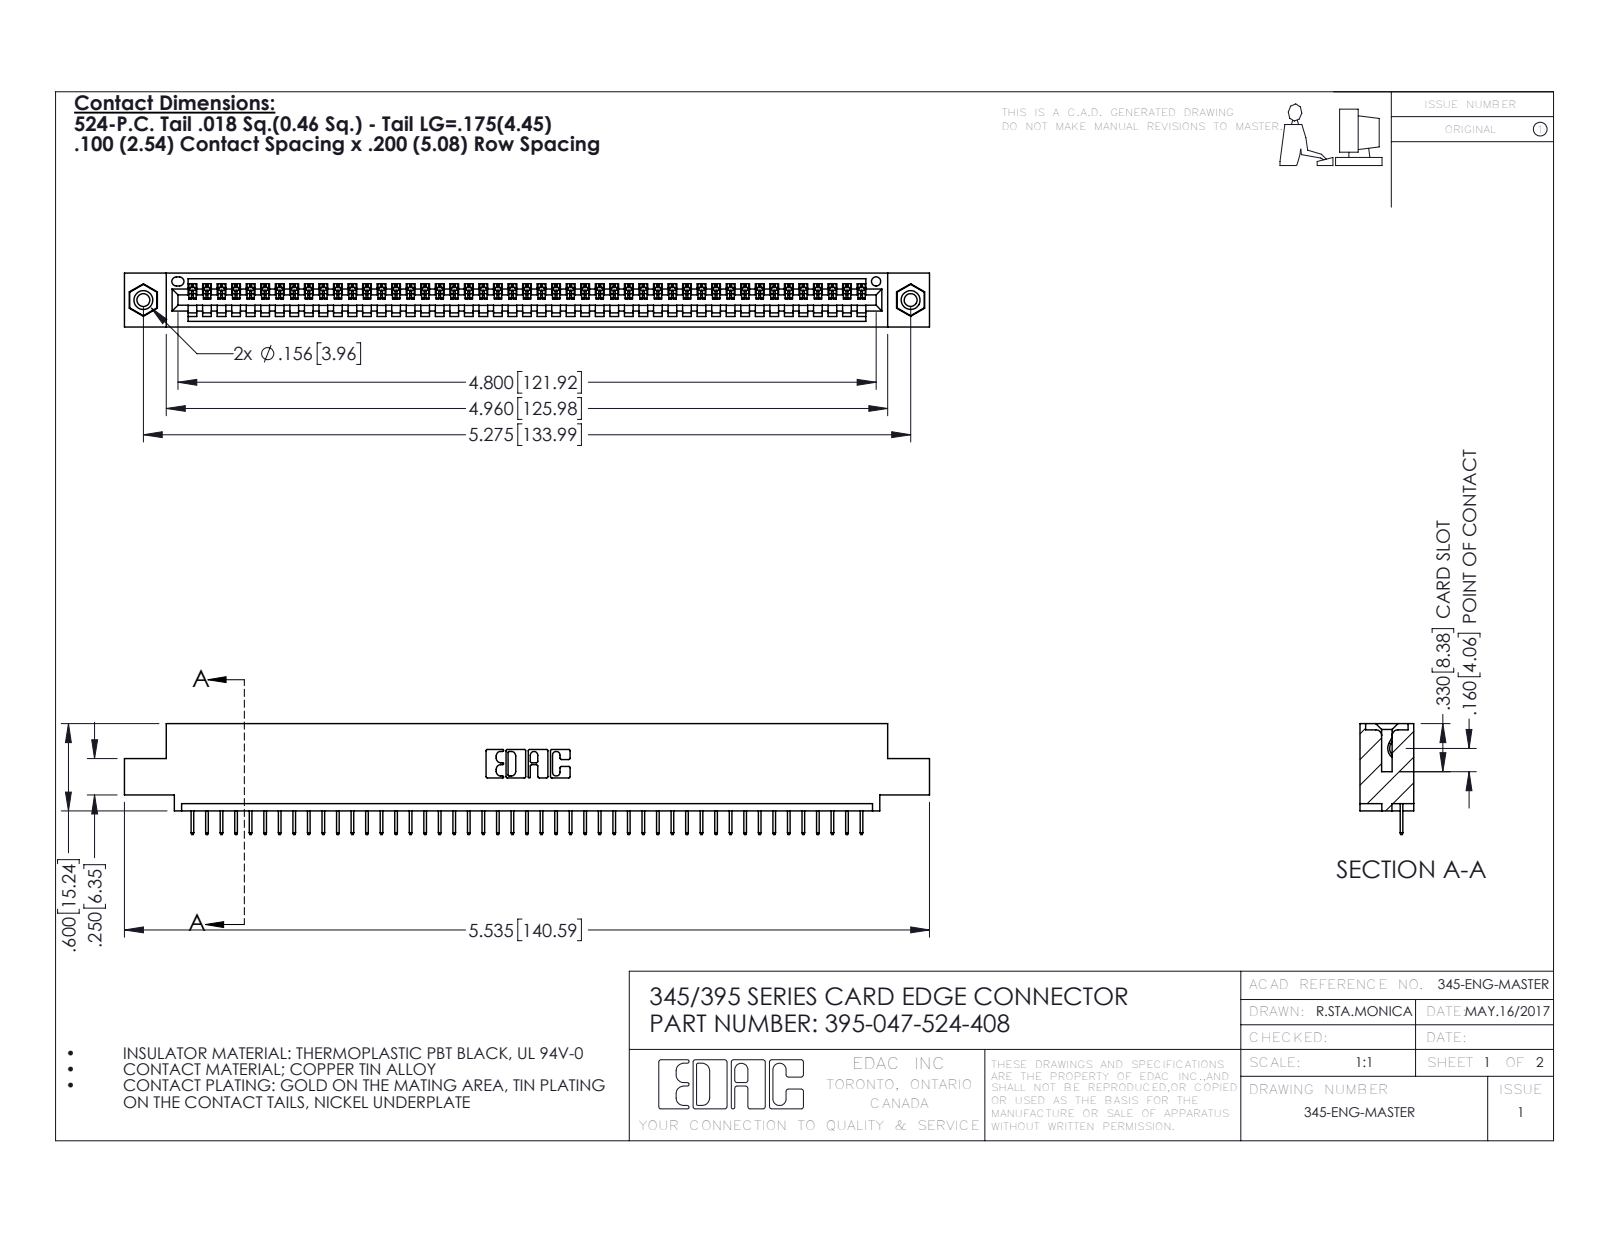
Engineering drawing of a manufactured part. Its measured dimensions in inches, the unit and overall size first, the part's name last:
Units: inches
Overall size (bounding box): 5.535 × 0.762 × 0.37
Round holes (diameter × count): ⌀0.089 ×2, ⌀0.125 ×2, ⌀0.156 ×2, ⌀0.064 ×1
Round bosses / shafts (diameter × count): ⌀0.155 ×2
Partial cylindrical surfaces — rounded edges, fillets, slot ends (radius × count): R0.006 ×94, R0.01 ×22, R0.007 ×6, R0.031 ×6, R0.026 ×3, R0.031 ×2, R0.04 ×2, R0.014 ×1
Main face-to-face distances: 0.072, 0.298, 0.37, 0.2, 0.098, 0.272, 0.025, 0.225, 0.072, 0.149
Hole centre spacings: 0.27, 5.039, 5.275
Volume: 0.801 in³ · Surface area: 26.38 in²
Bodies: 50 solids, 3104 faces (2278 planar, 810 cylindrical, 16 other)
Part name (STEP PRODUCT): 345-292-001_345-293-124; 345 Part_0.110 Offset - 0.156 Dia-TI; 395-047-524-408; 345-250-001_345-250-003-102
STEP written by: SolidWorks 2016 (CONFIG_CONTROL_DESIGN)
